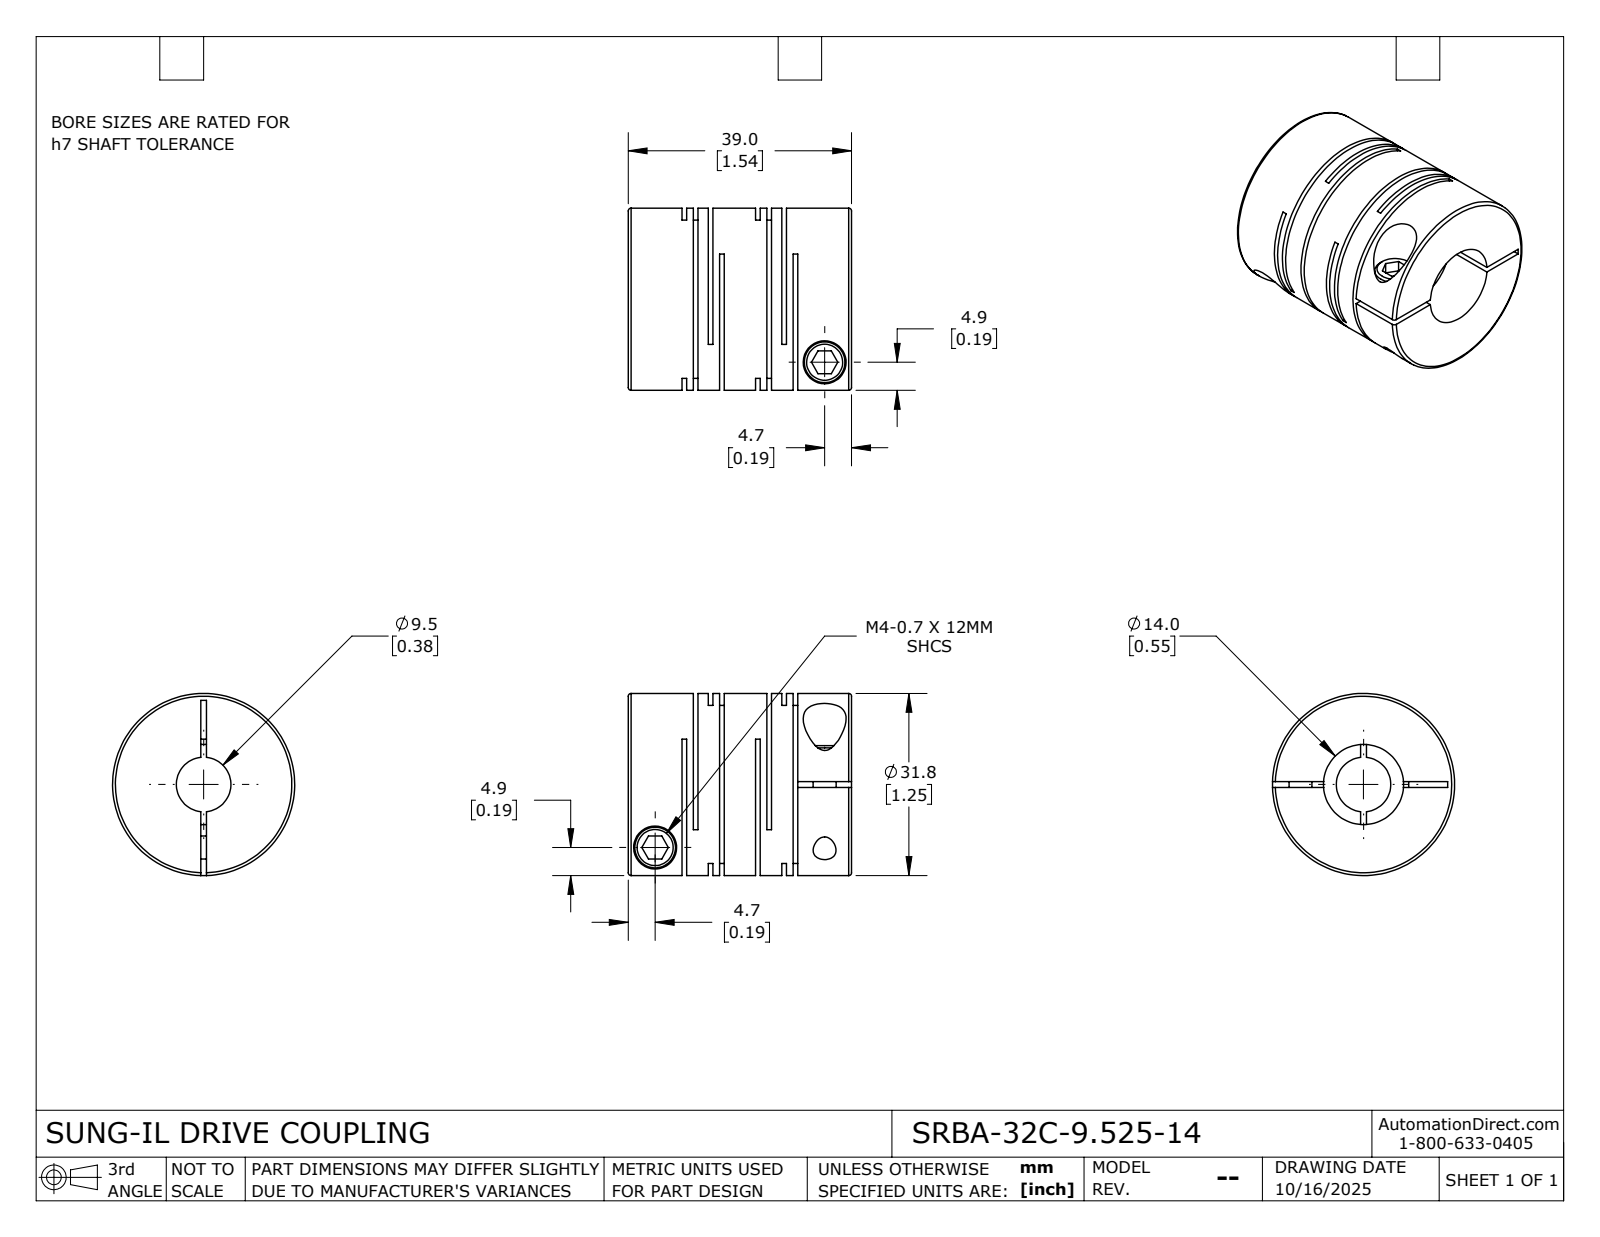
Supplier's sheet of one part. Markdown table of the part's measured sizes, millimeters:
| quantity | value |
| --- | --- |
| part name | SRBA-32C-9.525-14 |
| STEP written by | SolidWorks 2024 (CONFIG_CONTROL_DESIGN) |
| units | millimeters |
| bodies | 1 solid, 115 faces (60 planar, 42 cylindrical, 13 other) |
| overall size | 39 × 31.8 × 31.8 |
| volume | 21 782 mm³ |
| surface area | 15 231 mm² |
| round holes (diameter × count) | 4 × 2, 7.5 × 2, 9.53 × 1, 14 × 1 |
| round bosses / shafts (diameter × count) | 7.1 × 2, 31.8 × 1 |
| main face-to-face distances | 0.8, 12.84, 1.98, 4.58, 12.04, 1.18, 10.86, 3.78, 8.26, 2.6 |
